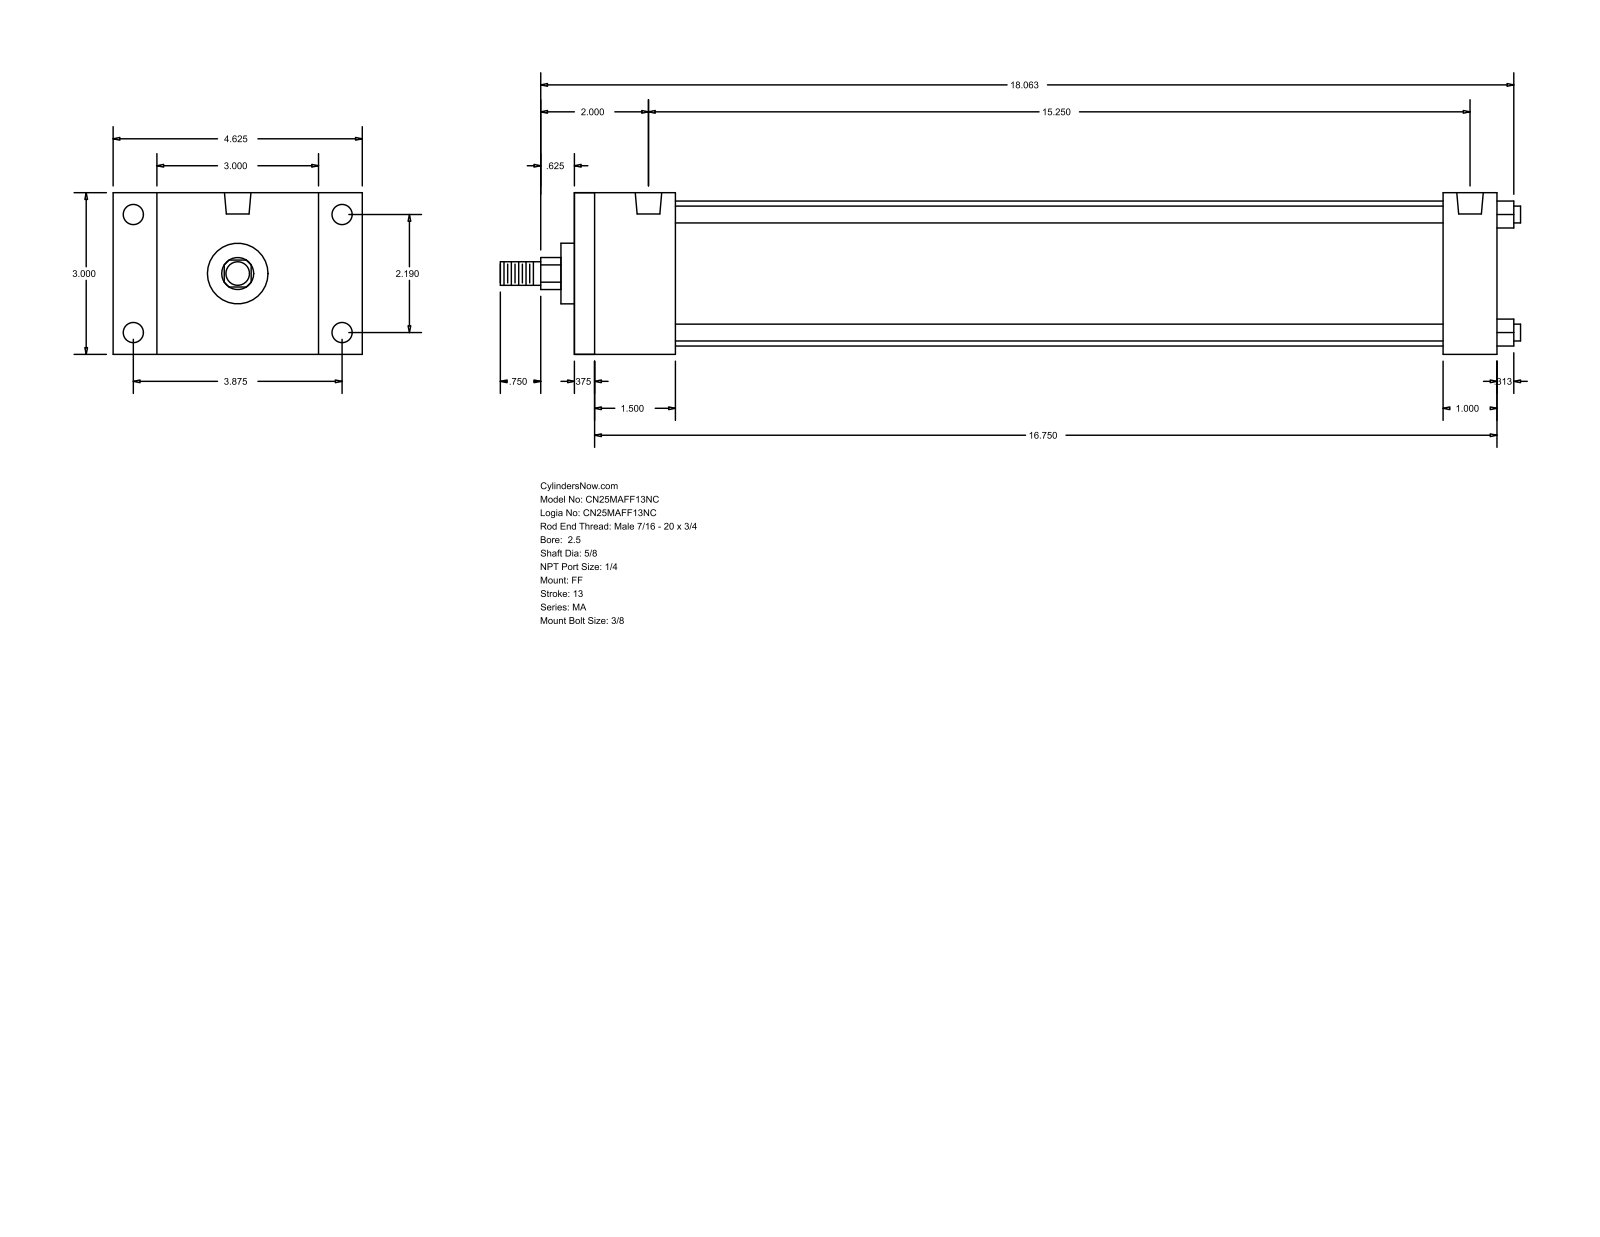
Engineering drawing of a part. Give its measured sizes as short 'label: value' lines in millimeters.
name: MA_FF__0250_0.625
written by: GSSL Pune (CONFIG_CONTROL_DESIGN)
unit: mm
bodies: 0 solids, 92 faces (64 planar, 28 cylindrical, 0 other)
size: 481.01 × 117.47 × 76.2
holes: 4× ⌀7.94, 4× ⌀9.53, 2× ⌀12.49
bosses: 4× ⌀7.94, 1× ⌀68.33, 1× ⌀28.57, 1× ⌀15.88, 1× ⌀11.11
rounds: 1× R7.54
face distances: 76.2, 434.97, 425.45, 9.52, 25.4, 47.62, 409.57, 38.1, 400.05, 361.95
hole spacings: 55.62, 98.42, 113.05, 387.35
